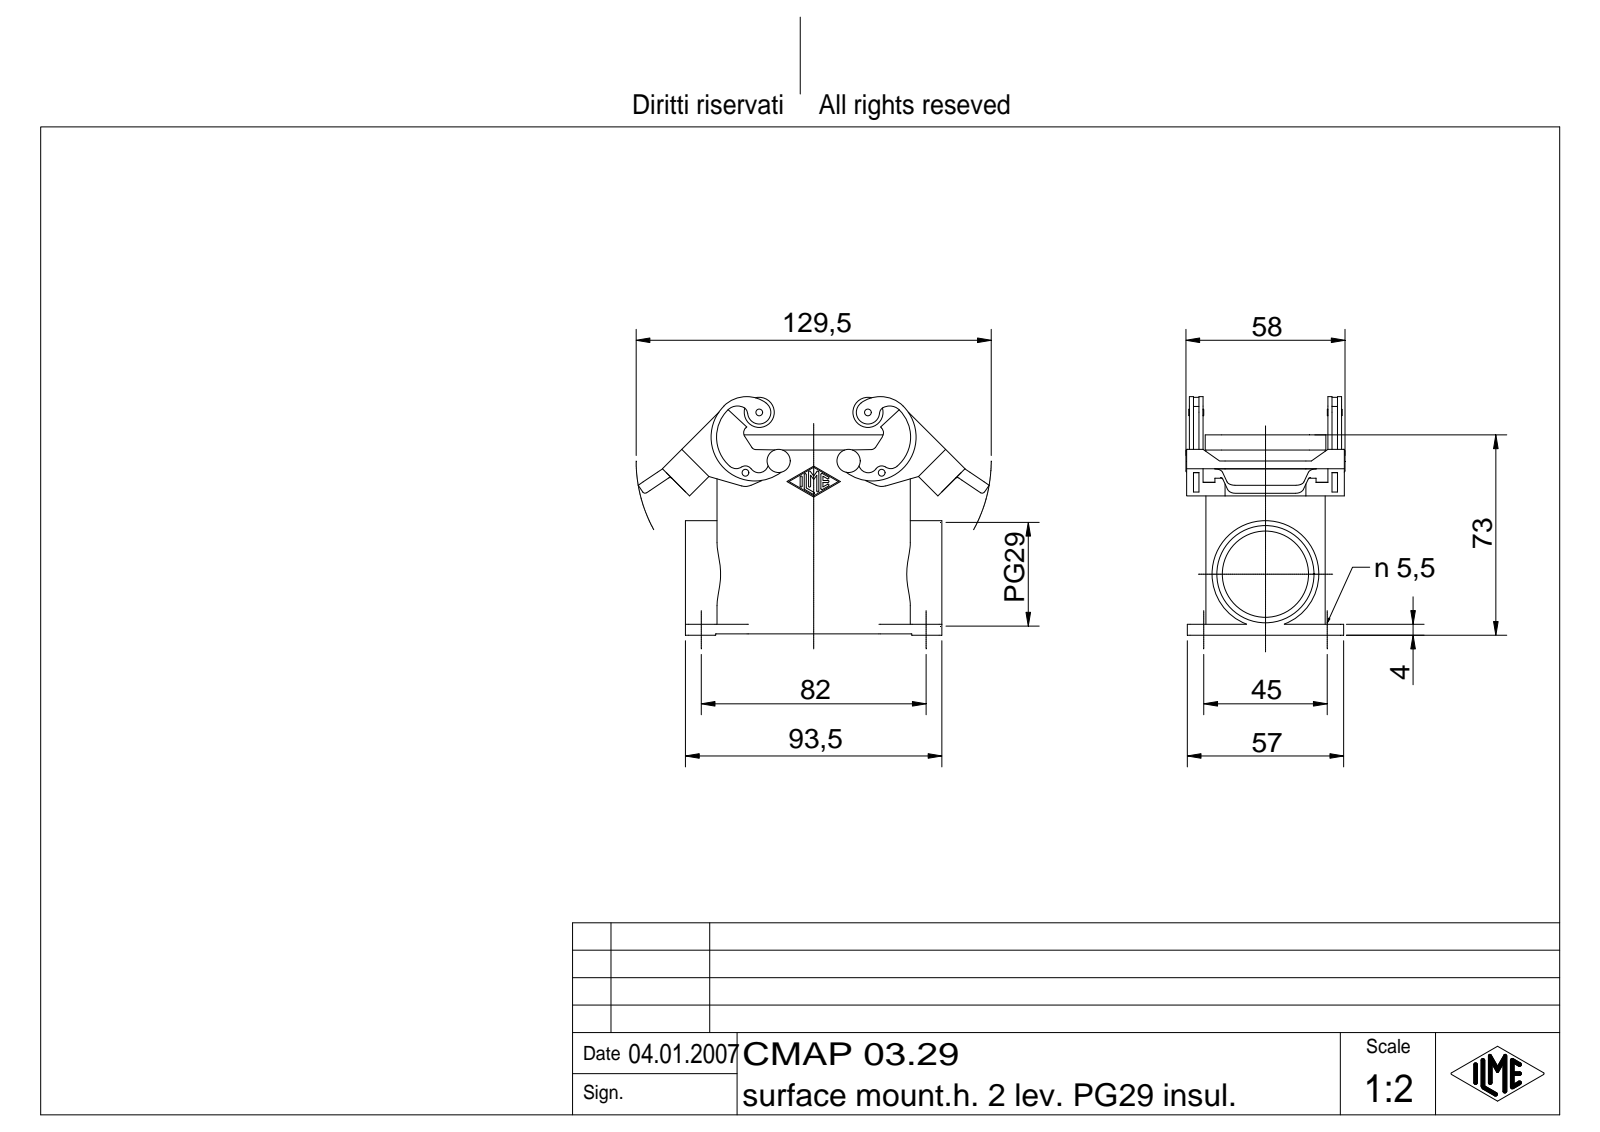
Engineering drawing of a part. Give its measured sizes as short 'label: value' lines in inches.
name: CMAP 03.29
written by: Autodesk Inventor 7 (AUTOMOTIVE_DESIGN)
unit: in
bodies: 1 solid, 753 faces (193 planar, 207 cylindrical, 353 other)
size: 5.039 × 3.423 × 2.283
volume: 6.08 in³; area: 92.66 in²
holes: 4× ⌀0.079, 4× ⌀0.217, 2× ⌀0.098, 1× ⌀1.239, 1× ⌀1.397
bosses: 2× ⌀0.433, 2× ⌀0.197, 2× ⌀0.118, 1× ⌀1.535
rounds: 20× R0.039, 14× R0.015, 12× R0.118, 8× R0.236, 6× R0.098, 4× R0.059, 4× R0.079, 4× R0.138
face distances: 0.118, 1.594, 1.713, 0.138, 1.476, 0.157, 1.988, 0.03, 0.177, 0.098
hole spacings: 0.888, 1.772, 1.96, 3.228, 3.683, 1.561, 1.956
